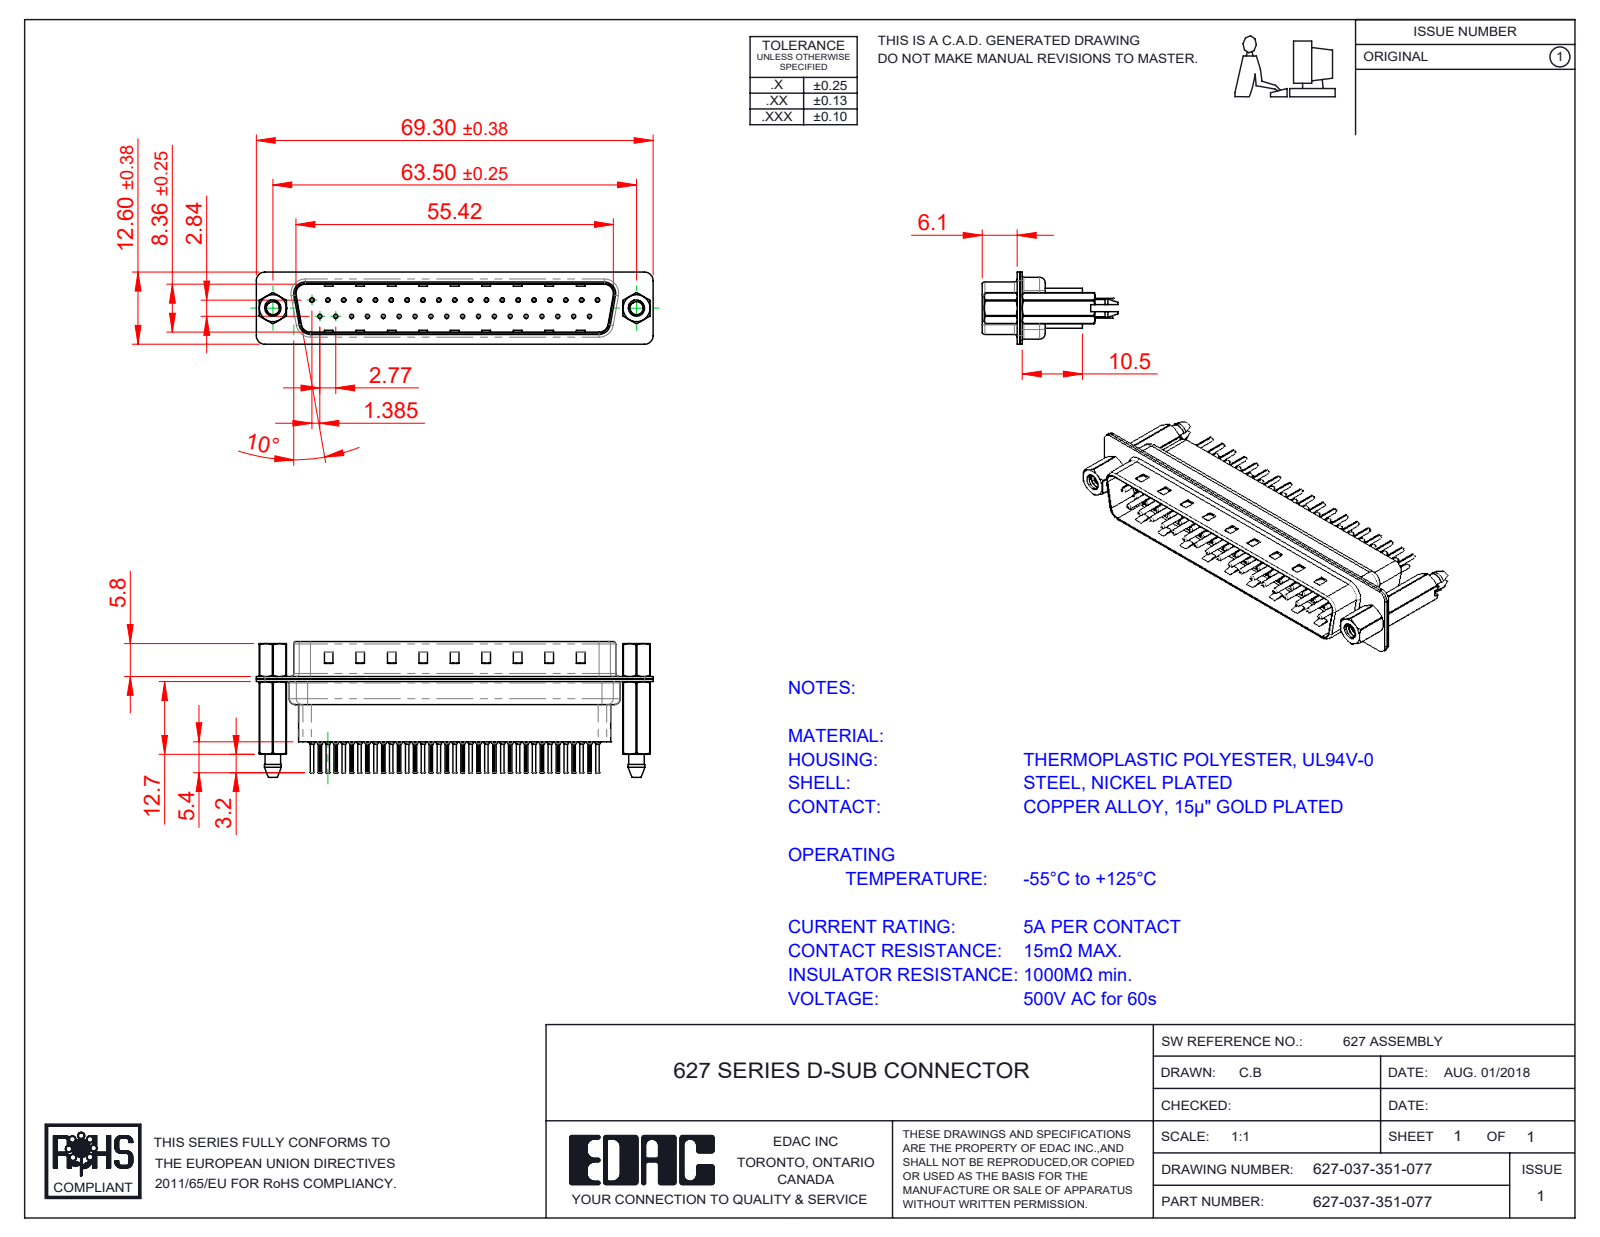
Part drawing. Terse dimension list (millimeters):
name: 627 Housing_37 HP; 627 Shell Front_37 Contacts; 627-037-351-077; 627 Shell Rear_37 Contacts (+4 more)
written by: SolidWorks 2020 (CONFIG_CONTROL_DESIGN)
unit: mm
bodies: 44 solids, 4272 faces (1145 planar, 1648 cylindrical, 1479 other)
size: 69.3 × 23.6 × 12.6
volume: 5 848 mm³; area: 14 927 mm²
holes: 37× ⌀0.2, 37× ⌀0.35, 37× ⌀1.1, 37× ⌀1.6, 2× ⌀2.26, 2× ⌀2.29, 2× ⌀4, 2× ⌀4.8
bosses: 37× ⌀2, 37× ⌀1.5, 37× ⌀0.75, 37× ⌀0.6, 2× ⌀4.9, 2× ⌀2.79
rounds: 74× R0.1, 18× R1.5, 12× R2, 10× R1.6, 8× R0.5, 4× R0.25, 4× R0.6, 4× R0.65
face distances: 0.4, 0.82, 9.58, 0.45, 0.68, 7.68, 1.5, 1.08, 8.08, 8.76
hole spacings: 3.16, 2.77, 5.54, 8.31, 5.04, 10.1, 11.08, 12.78
